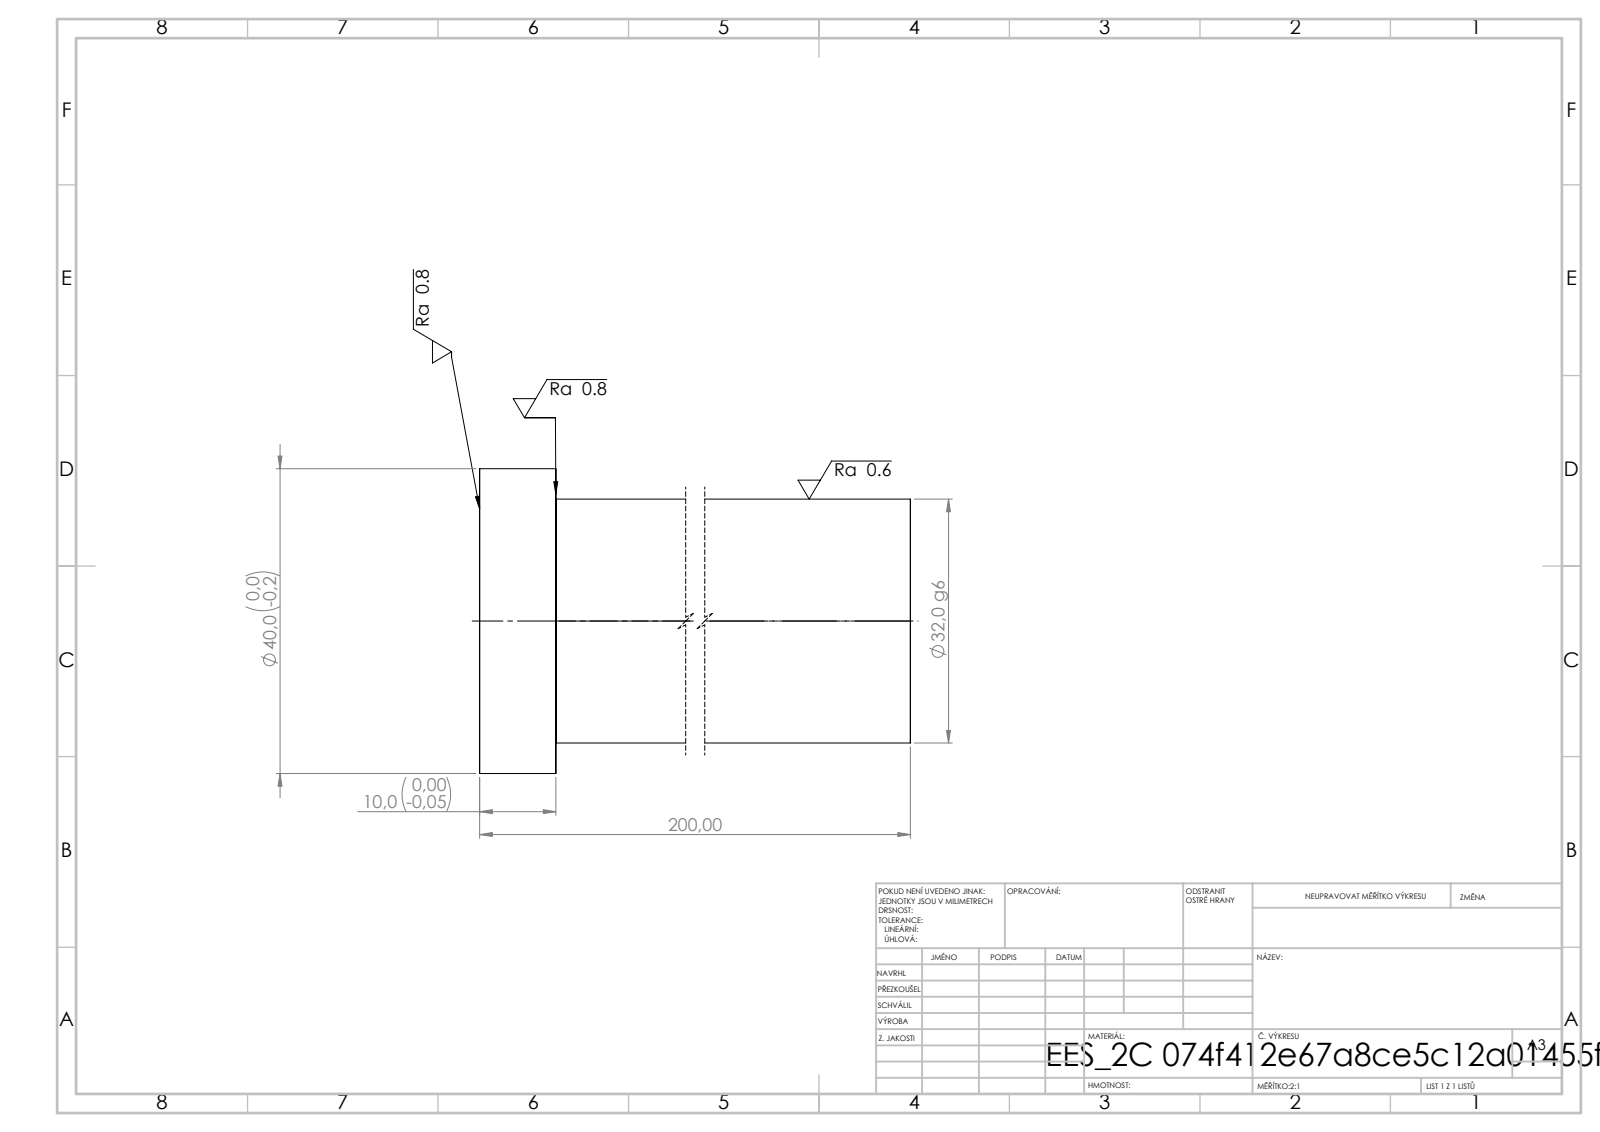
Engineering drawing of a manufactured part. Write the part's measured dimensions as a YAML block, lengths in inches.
step_written_by: "SolidWorks 2019 (CONFIG_CONTROL_DESIGN)"
units: inches
bodies: {solids: 1, faces: 7, planar: 3, cylindrical: 4, other: 0}
overall_size: [7.874, 1.575, 1.575]
volume: 10.09
surface_area: 35.45
round_bosses_or_shafts:
  - {diameter: 1.575, count: 1}
  - {diameter: 1.26, count: 1}
face_to_face_distances: [7.874, 0.394, 7.48]
